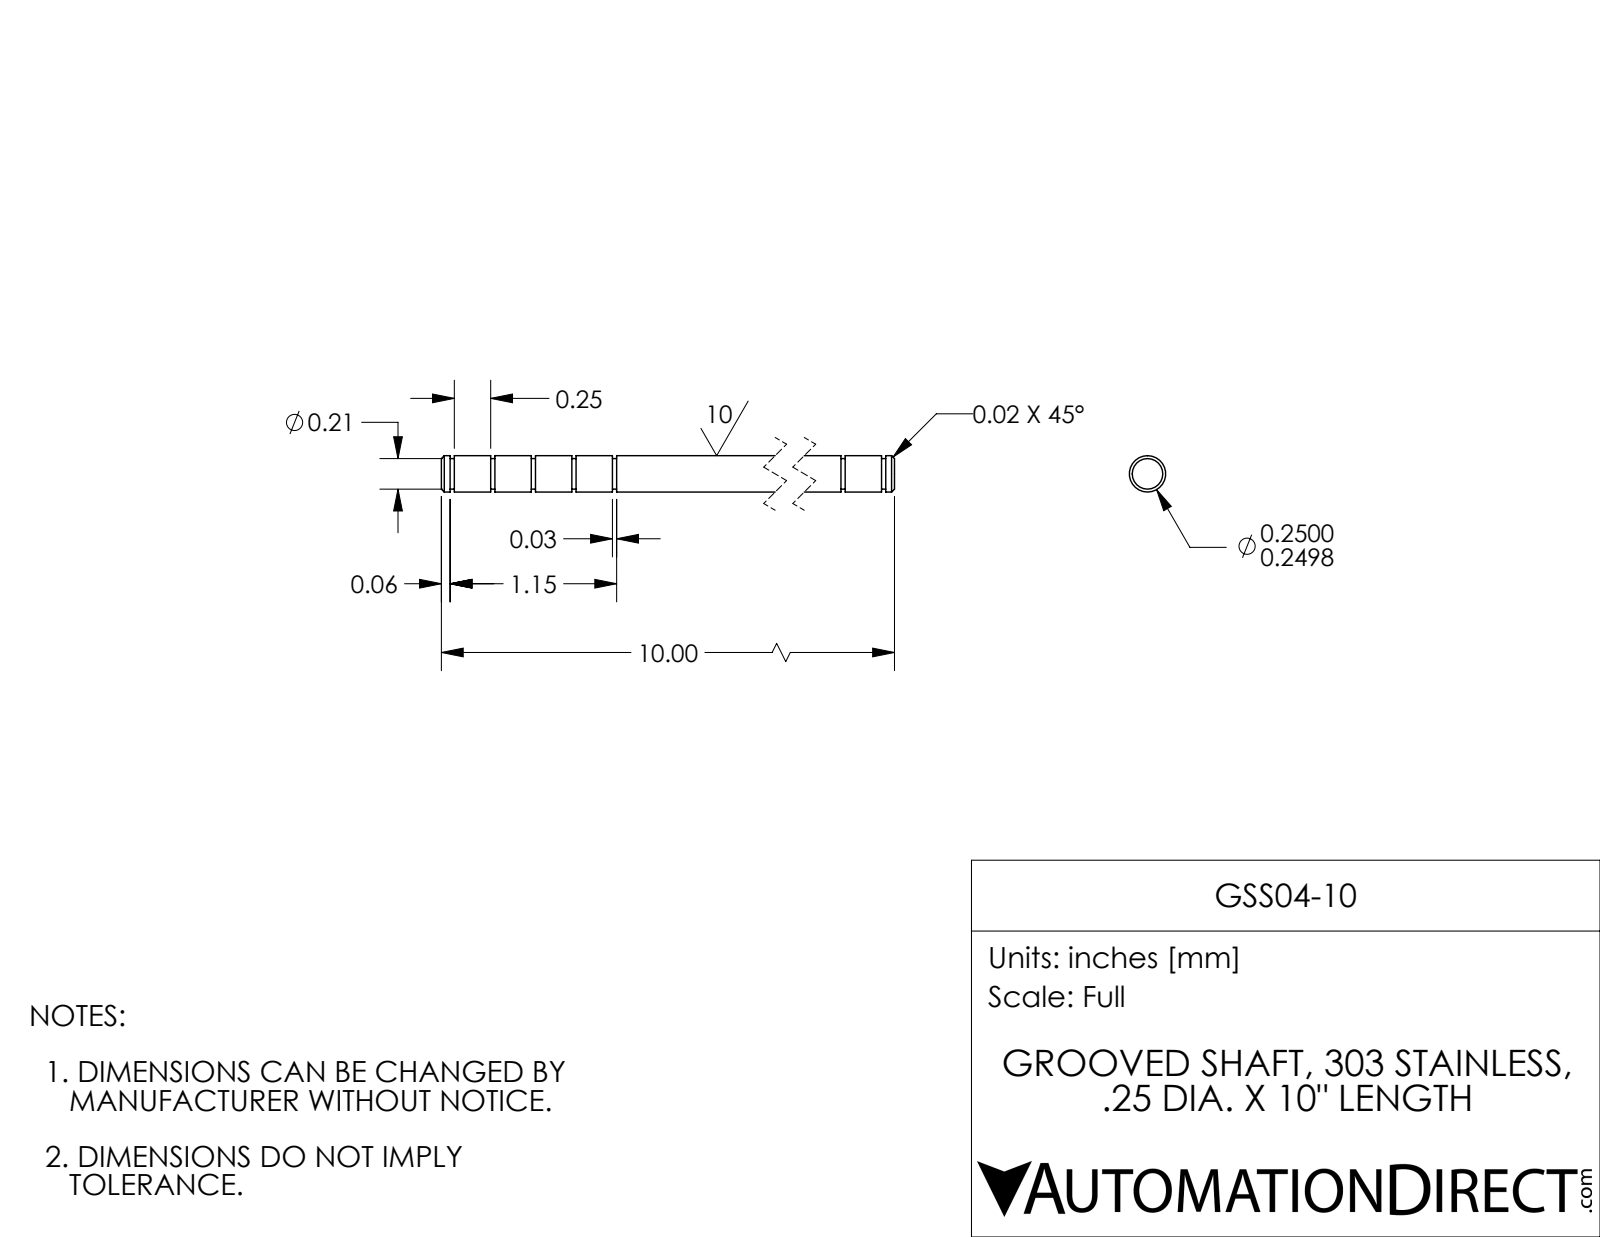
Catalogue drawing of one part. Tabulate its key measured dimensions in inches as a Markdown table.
| quantity | value |
| --- | --- |
| part name | GSS04-10 |
| STEP written by | SolidWorks 2017 (AUTOMOTIVE_DESIGN) |
| units | inches |
| bodies | 1 solid, 50 faces (16 planar, 30 cylindrical, 4 other) |
| overall size | 10 × 0.25 × 0.25 |
| volume | 0.488 in³ |
| surface area | 8.11 in² |
| round bosses / shafts (diameter × count) | 0.25 × 1, 0.21 × 1 |
| main face-to-face distances | 0.279, 0.029, 0.25, 0.837, 9.572, 0.558, 8.735, 9.293, 9.014, 0.308 |
